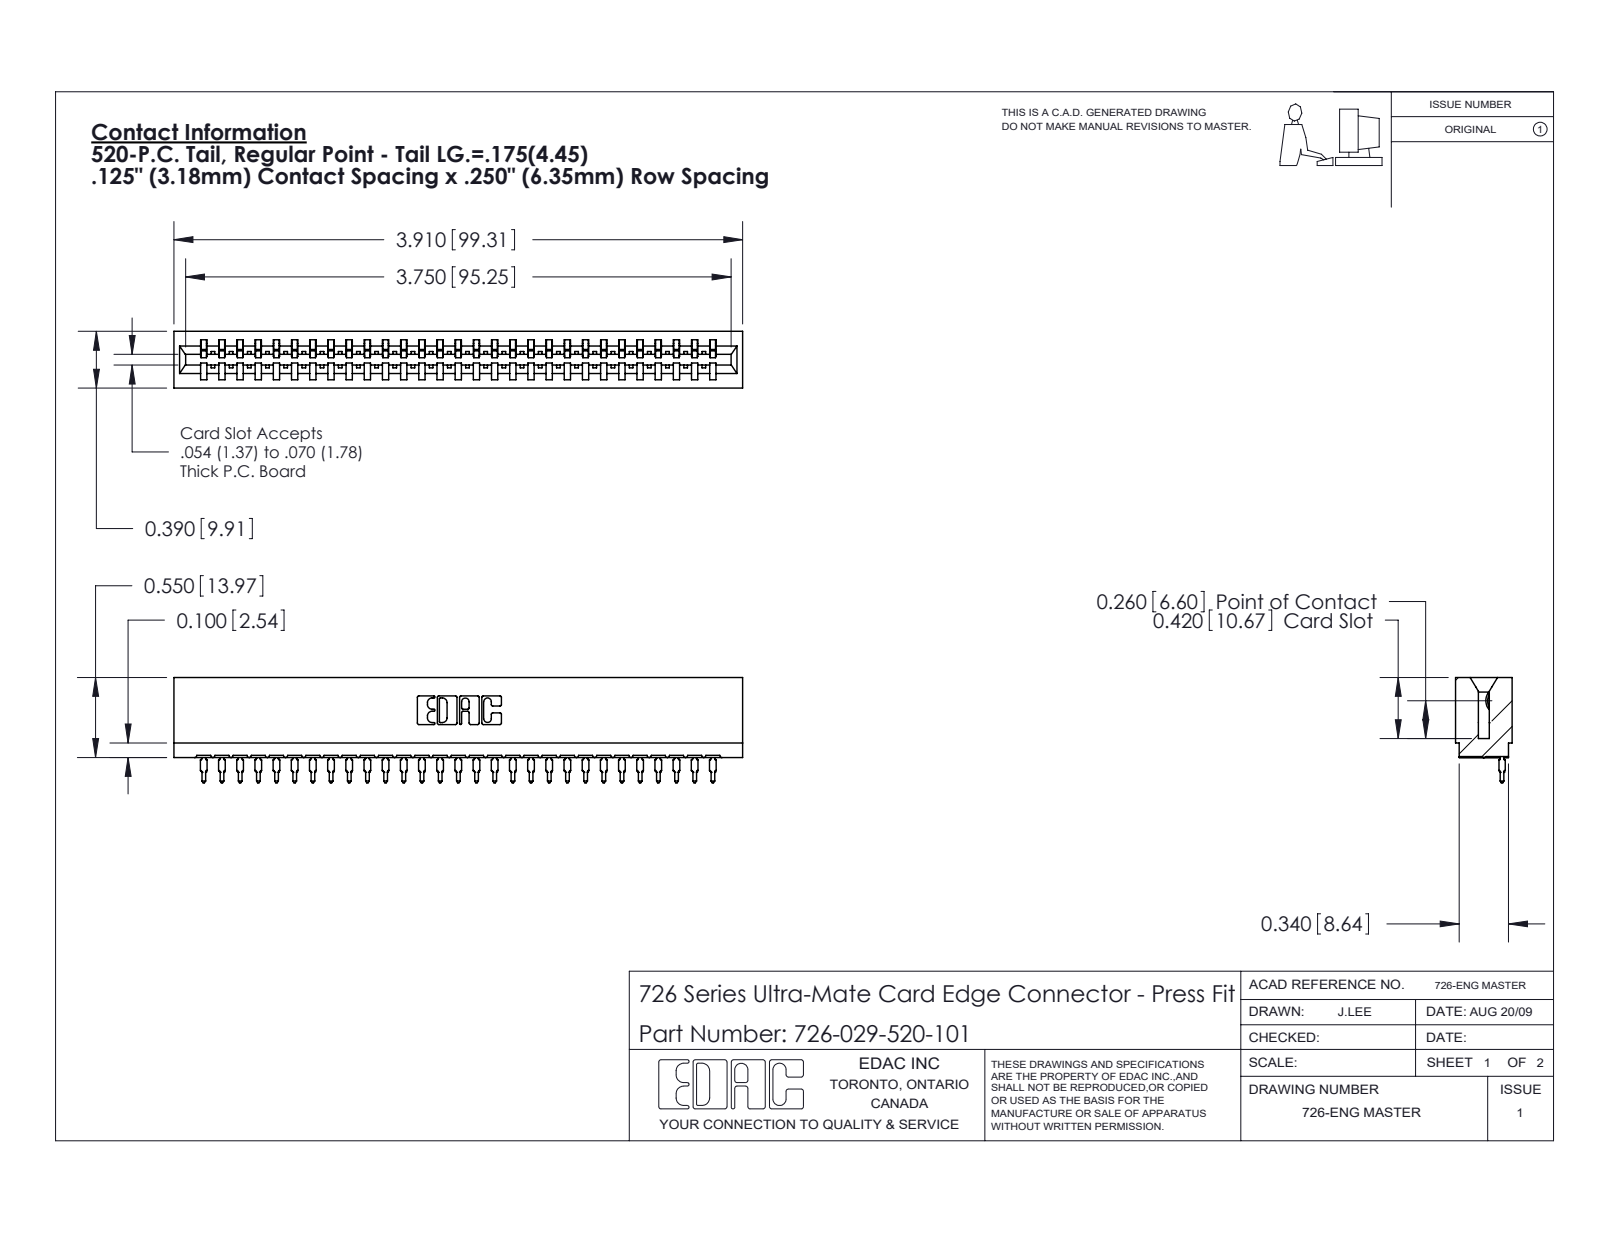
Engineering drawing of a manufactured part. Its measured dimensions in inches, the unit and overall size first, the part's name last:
Units: inches
Overall size (bounding box): 3.91 × 0.724 × 0.39
Partial cylindrical surfaces — rounded edges, fillets, slot ends (radius × count): R0.021 ×58, R0.015 ×30, R0.01 ×22, R0.007 ×6, R0.031 ×6, R0.005 ×4, R0.011 ×4, R0.026 ×3
Main face-to-face distances: 0.057, 0.333, 0.39, 0.025, 0.307, 0.25, 0.5, 0.275, 0.75, 0.365
Volume: 0.543 in³ · Surface area: 20.44 in²
Bodies: 30 solids, 3229 faces (1882 planar, 593 cylindrical, 754 other)
Part name (STEP PRODUCT): 726-029-520-101; 726 Part_.515 Slot Depth - 01; 746-292-001_520
STEP written by: SolidWorks 2020 (CONFIG_CONTROL_DESIGN)
